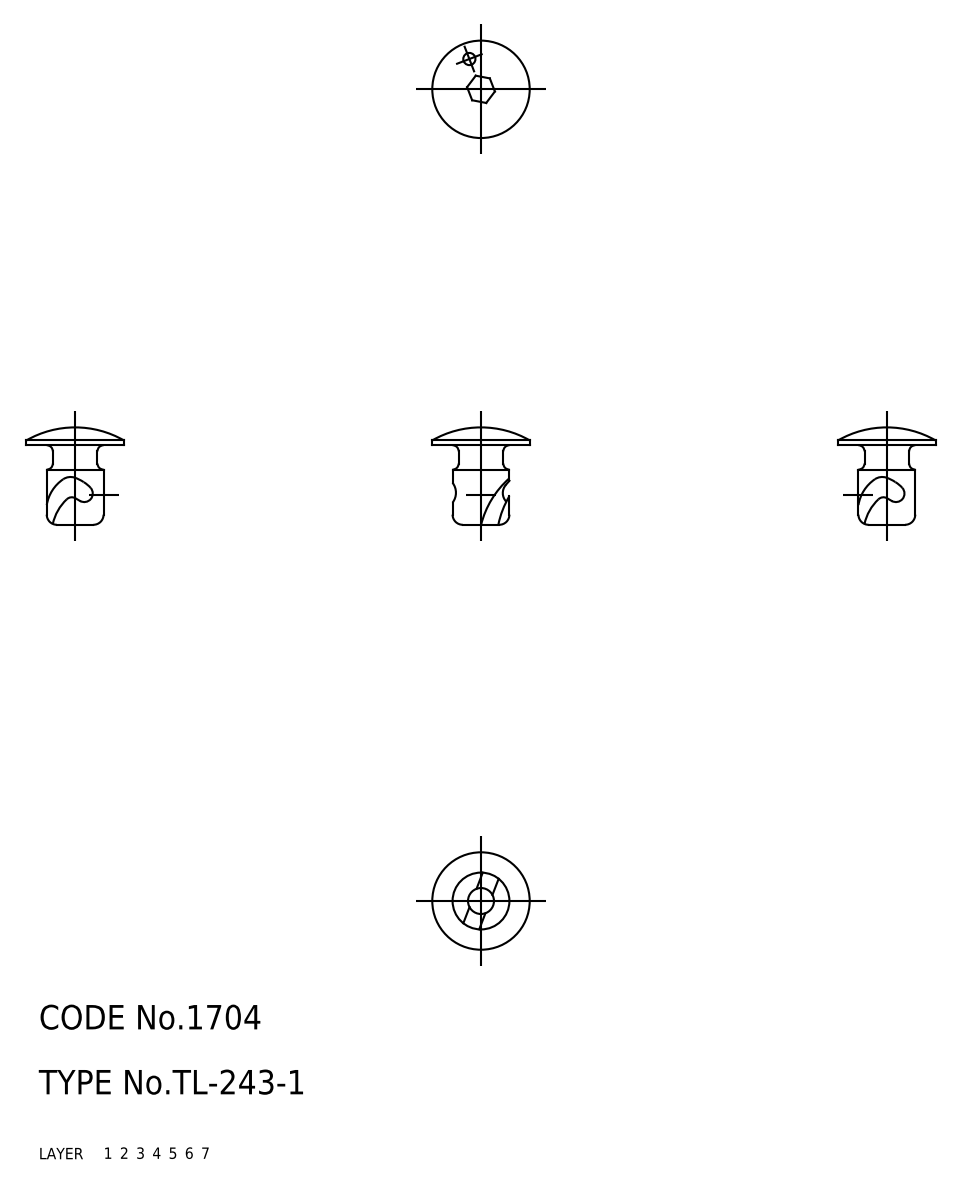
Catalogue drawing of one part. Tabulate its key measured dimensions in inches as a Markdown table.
| quantity | value |
| --- | --- |
| part name | fastener |
| STEP written by | CADfix (AUTOMOTIVE_DESIGN) |
| units | inches |
| bodies | 1 solid, 36 faces (0 planar, 0 cylindrical, 36 other) |
| overall size | 0.472 × 0.472 × 0.469 |
| volume | 0.022 in³ |
| surface area | 0.856 in² |
